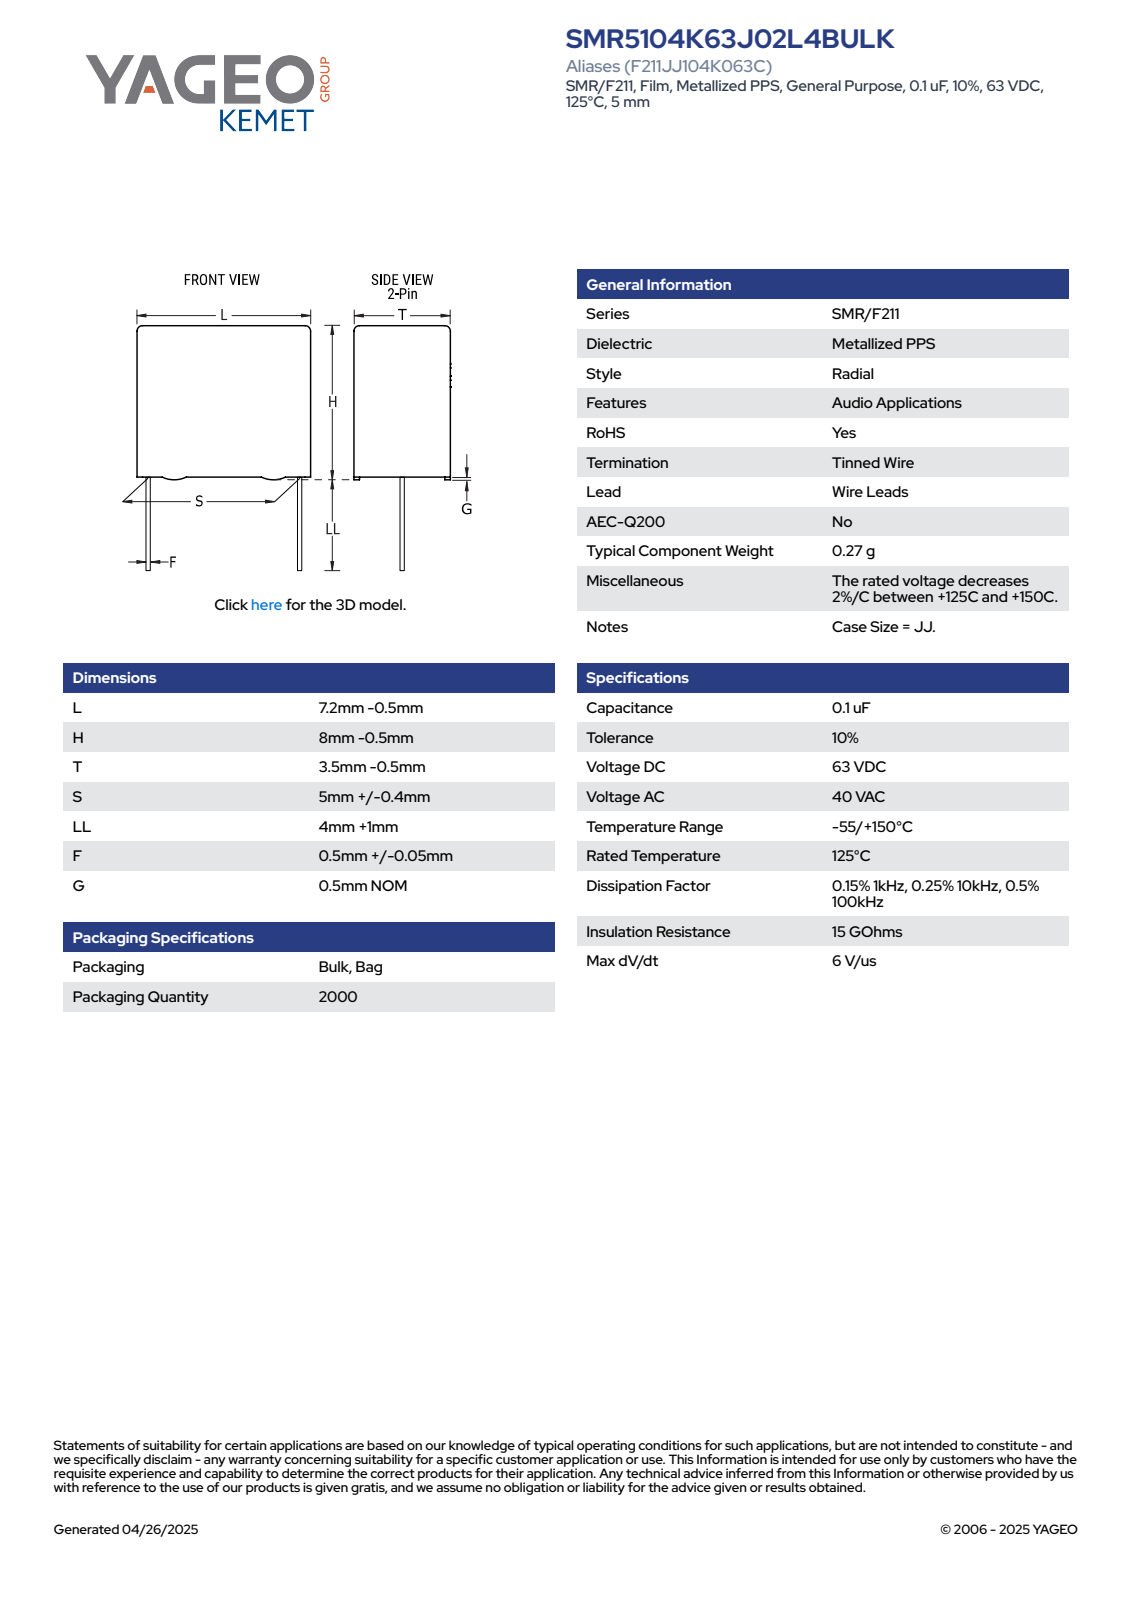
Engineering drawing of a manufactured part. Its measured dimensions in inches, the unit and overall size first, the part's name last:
Units: inches
Overall size (bounding box): 0.492 × 0.264 × 0.118
Round bosses / shafts (diameter × count): ⌀0.022 ×2
Partial cylindrical surfaces — rounded edges, fillets, slot ends (radius × count): R0.02 ×4
Main face-to-face distances: 0.118, 0.264, 0.276, 0.111, 0.105, 0.02, 0.295, 0.197, 0.217, 0.492
Volume: 0.009 in³ · Surface area: 0.312 in²
Bodies: 4 solids, 89 faces (81 planar, 8 cylindrical, 0 other)
Part name (STEP PRODUCT): CFR_RBG_7.2X8X3.5_L6.7H7.5T3S5LL5F0.55G0.5
STEP written by: SolidWorks 2021 (AUTOMOTIVE_DESIGN)
